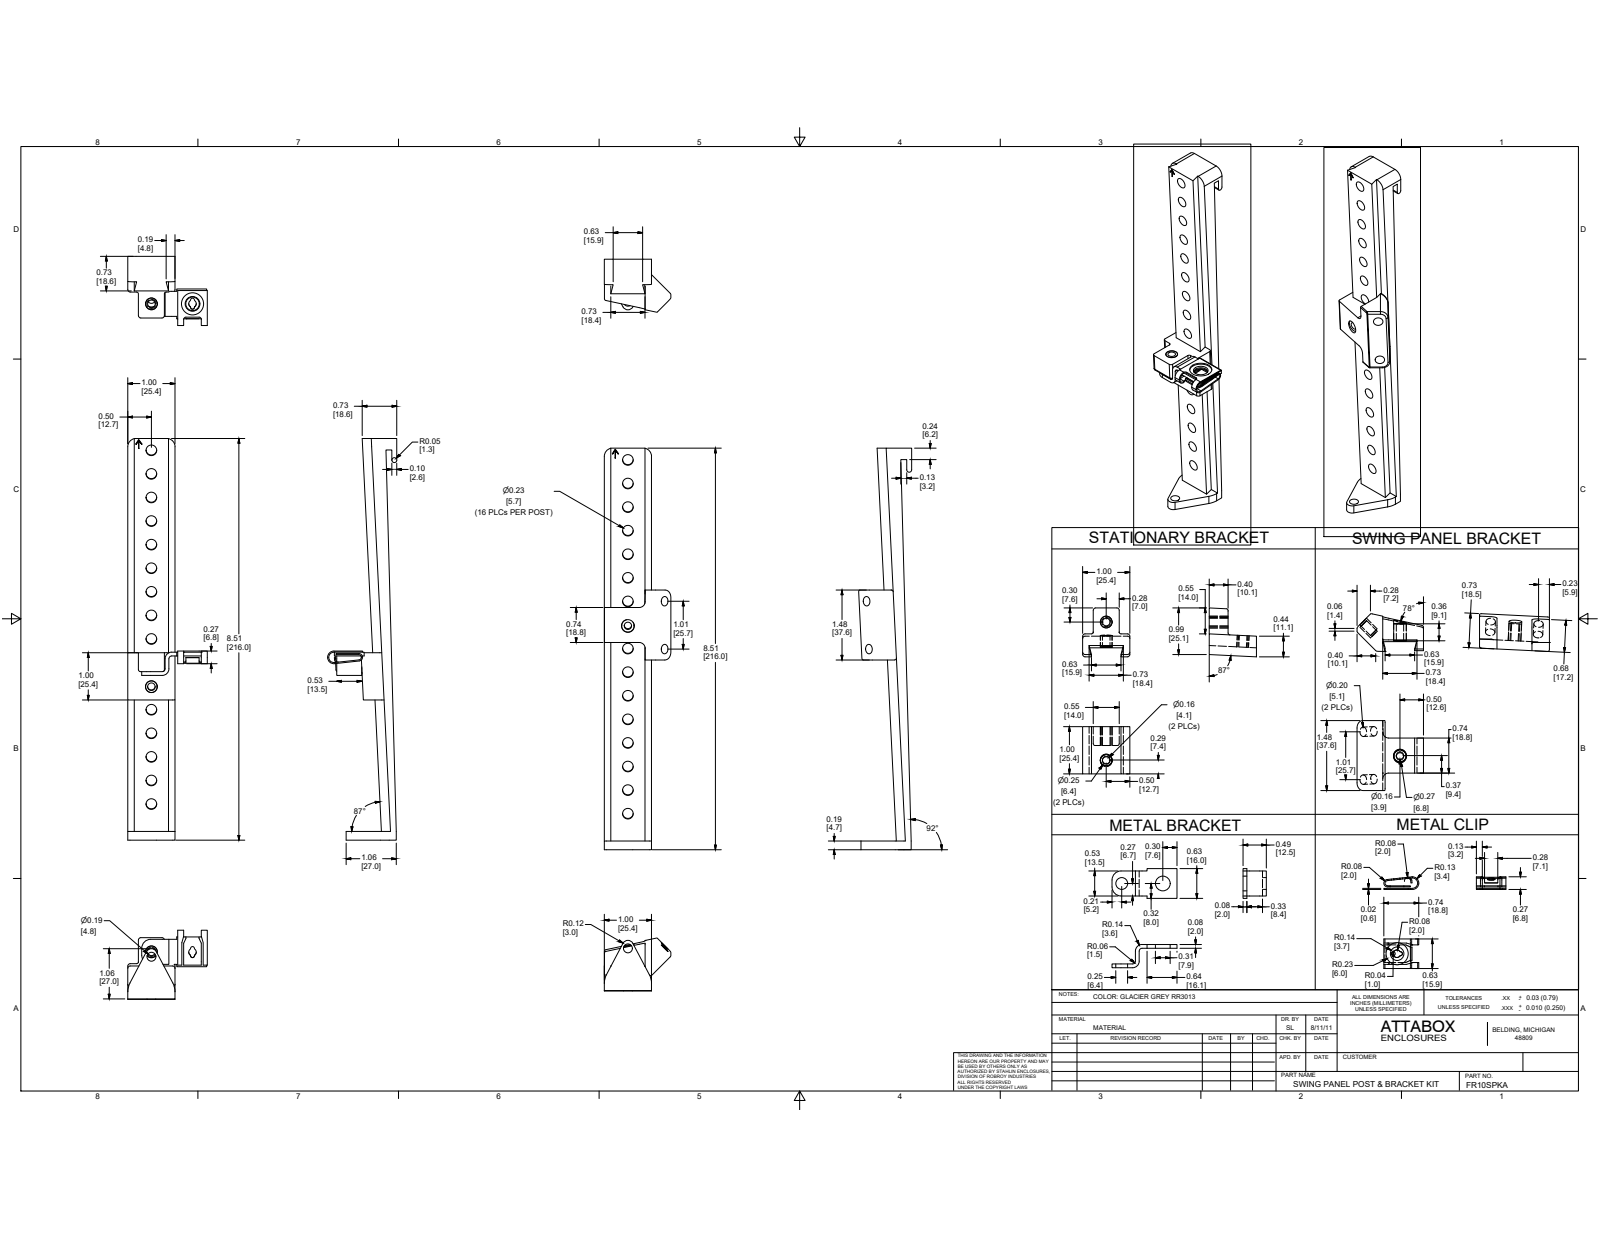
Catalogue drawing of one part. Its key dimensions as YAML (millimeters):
part_name: "FR10SPKA"
step_written_by: "SolidWorks 2019 (AUTOMOTIVE_DESIGN)"
units: millimeters
bodies: {solids: 32, faces: 2500, planar: 1328, cylindrical: 434, other: 738}
overall_size: [527.2, 425.5, 221.7]
volume: 235300
surface_area: 112600
round_holes:
  - {diameter: 6.4, count: 66}
  - {diameter: 4, count: 6}
  - {diameter: 6.4, count: 6}
  - {diameter: 5.5, count: 4}
  - {diameter: 5.6, count: 4}
  - {diameter: 7.9, count: 3}
  - {diameter: 8.9, count: 2}
round_bosses_or_shafts:
  - {diameter: 4.8, count: 10}
  - {diameter: 9.5, count: 6}
  - {diameter: 6.2, count: 6}
  - {diameter: 11, count: 4}
  - {diameter: 8, count: 4}
partial_cylinders:
  - {radius: 0.3, count: 204}
  - {radius: 1.5, count: 40}
  - {radius: 1.6, count: 18}
  - {radius: 0.6, count: 8}
  - {radius: 3.3, count: 8}
  - {radius: 1.2, count: 4}
  - {radius: 4.8, count: 4}
  - {radius: 5.8, count: 4}
face_to_face_distances: [610.1, 25.4, 256.4, 353.7, 281.8, 328.3, 71.8, 5.2, 261.6, 287]
hole_center_spacings: [12.7, 73, 25.4, 76.2, 38.1, 81.3, 50.8, 88]
